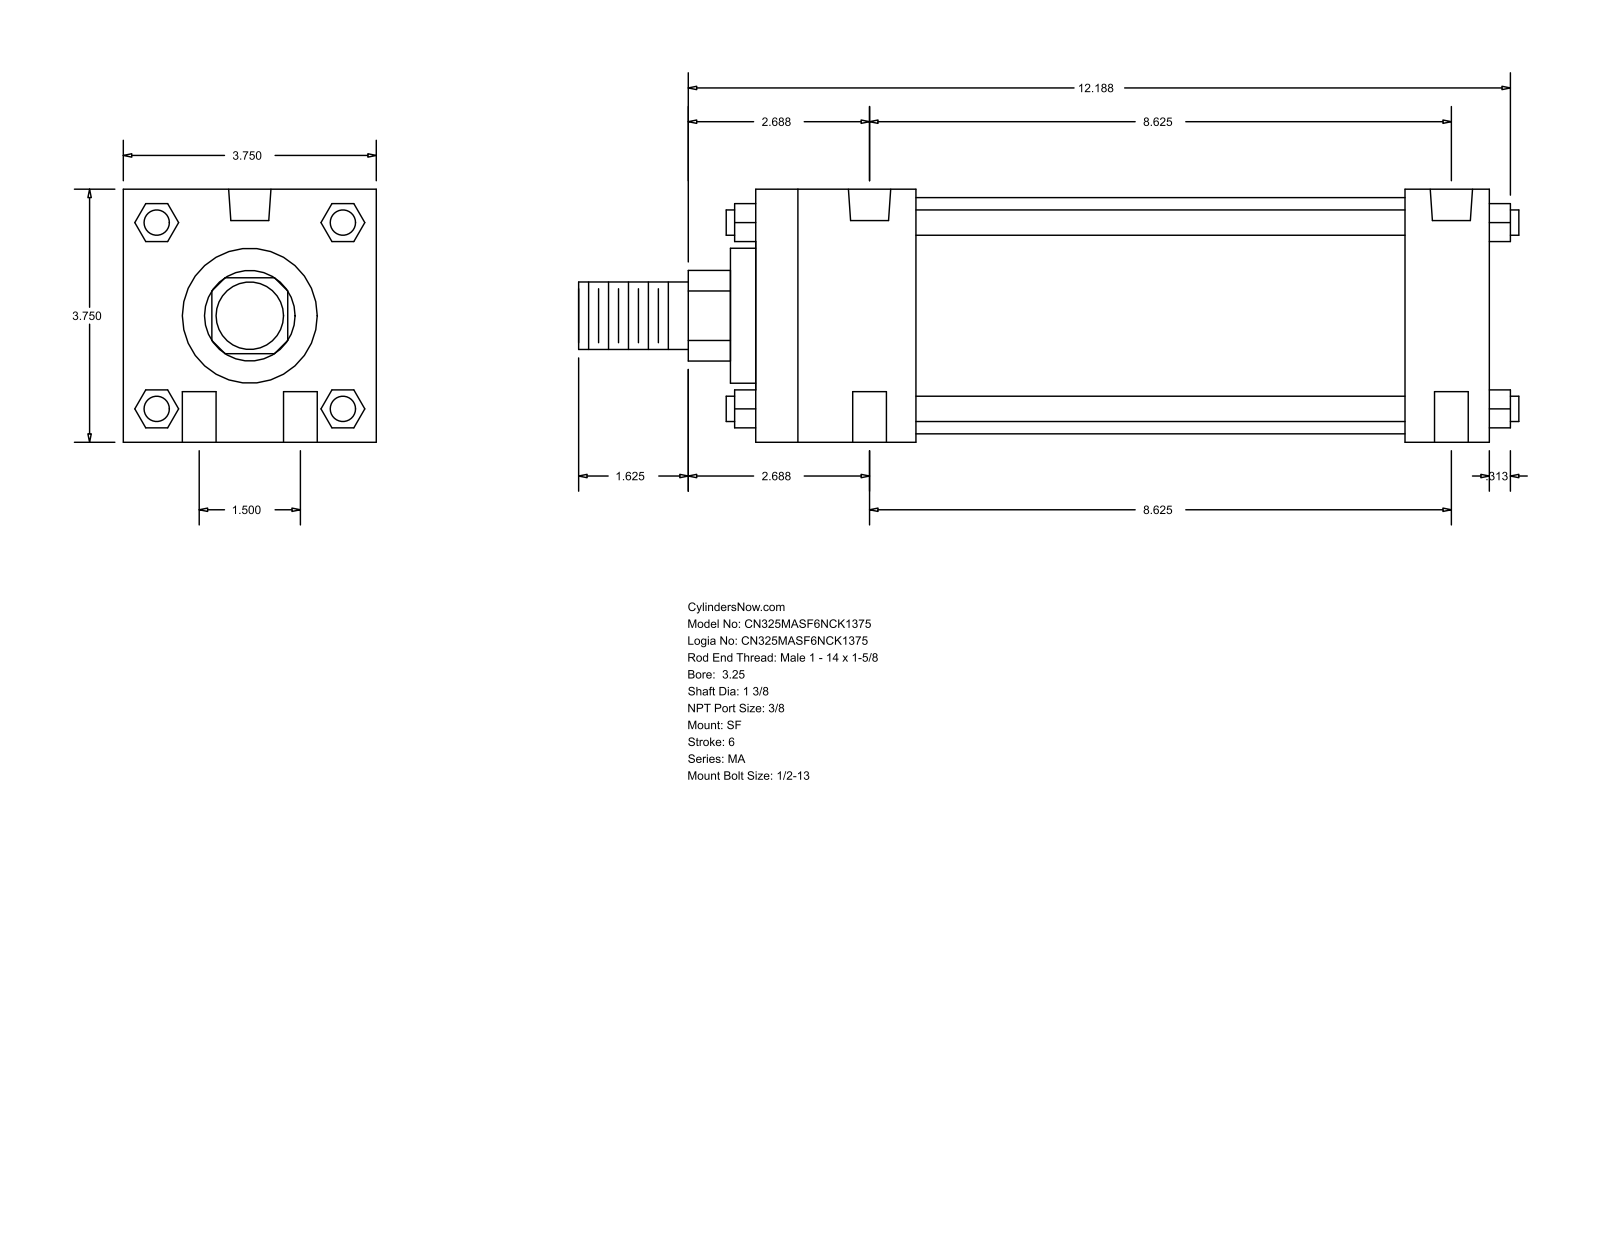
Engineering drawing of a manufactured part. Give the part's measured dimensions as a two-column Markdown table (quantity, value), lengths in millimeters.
| quantity | value |
| --- | --- |
| part name | MA_SF__0325_1.375 |
| STEP written by | GSSL Pune (CONFIG_CONTROL_DESIGN) |
| units | millimeters |
| bodies | 0 solids, 124 faces (94 planar, 30 cylindrical, 0 other) |
| overall size | 354.01 × 95.25 × 95.25 |
| round holes (diameter × count) | 12.7 × 4, 11.11 × 2, 15.93 × 2 |
| round bosses / shafts (diameter × count) | 9.53 × 4, 88.9 × 1, 50.8 × 1, 34.92 × 1, 25.4 × 1 |
| partial cylindrical surfaces (radius × count) | 17.06 × 1 |
| main face-to-face distances | 95.24, 276.22, 244.48, 31.74, 60.32, 184.16, 215.9, 9.52, 69.84, 254 |
| hole center spacings | 19.05, 219.91, 219.08, 38.1, 222.37, 209.54 |
